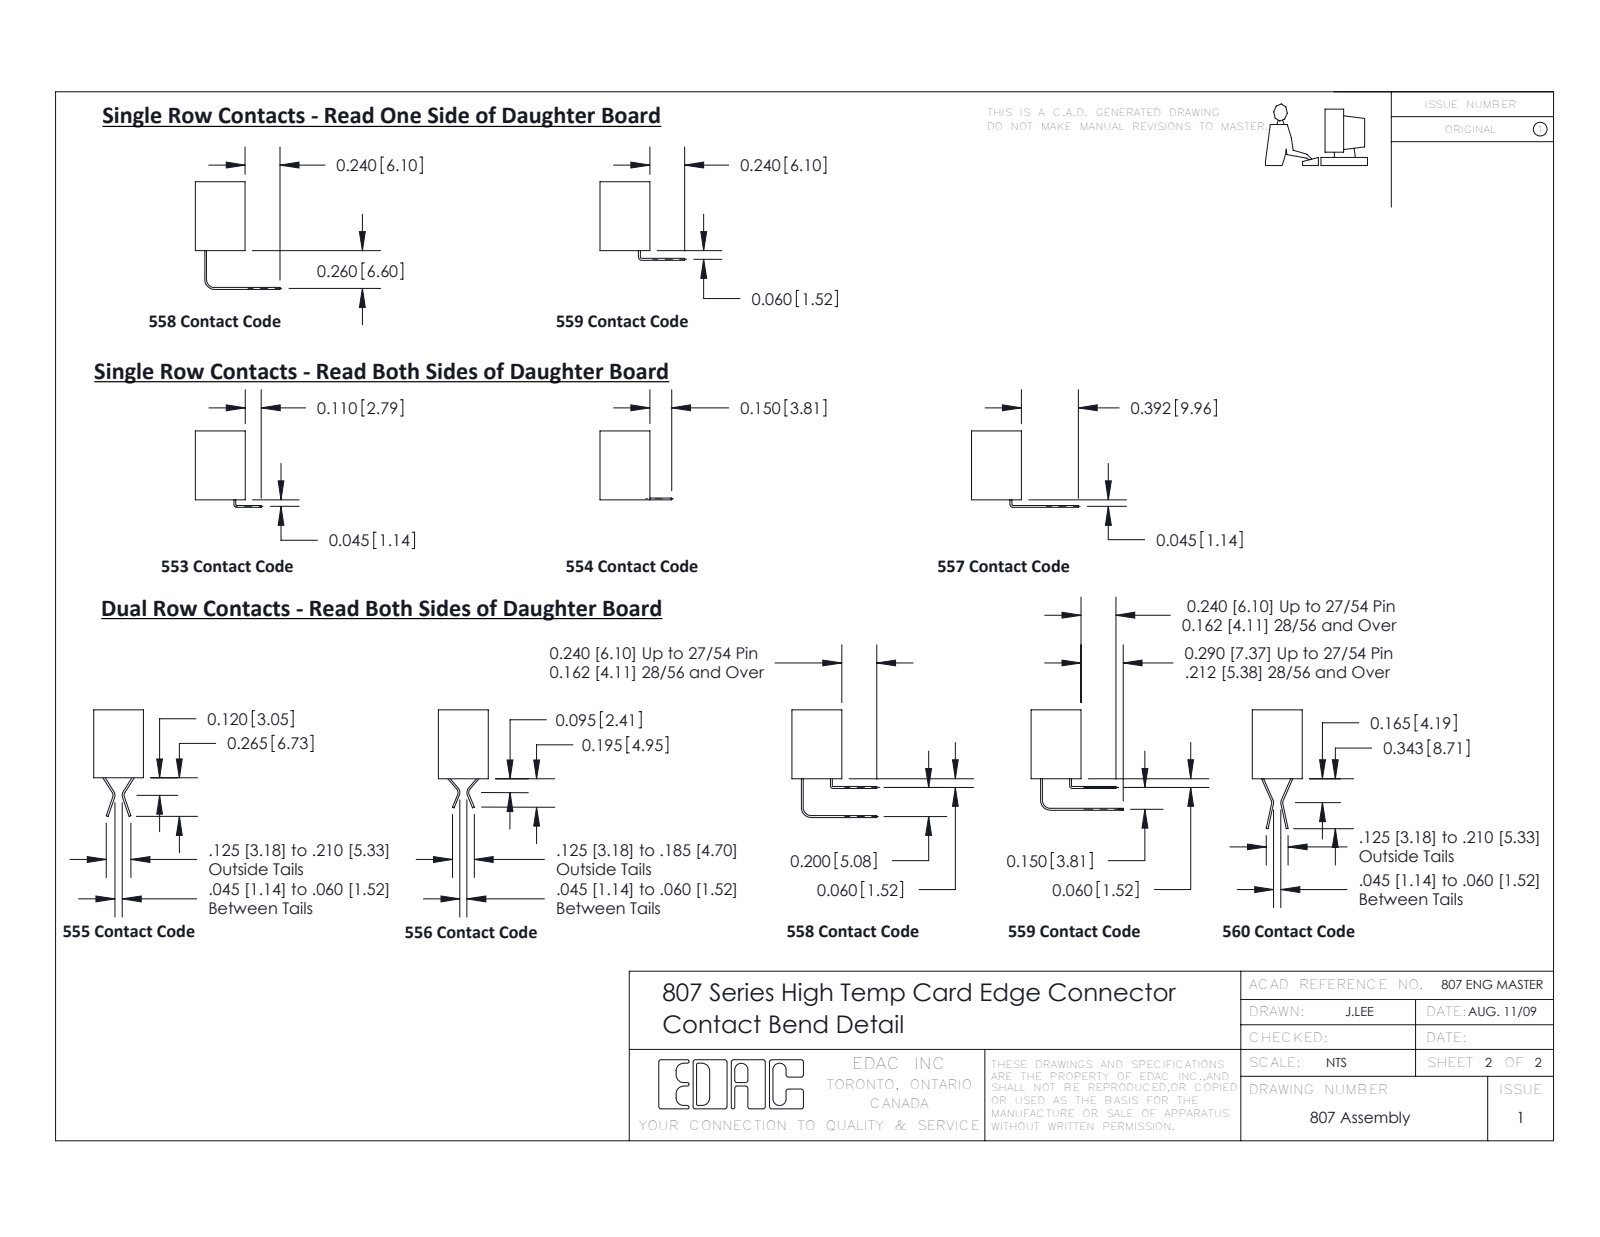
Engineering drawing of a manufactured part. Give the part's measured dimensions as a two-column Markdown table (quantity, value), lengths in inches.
| quantity | value |
| --- | --- |
| part name | 307-290-001_505; 357-006-405-101; 307 Part_No Mounting Lugs |
| STEP written by | SolidWorks 2020 (CONFIG_CONTROL_DESIGN) |
| units | inches |
| bodies | 7 solids, 453 faces (282 planar, 157 cylindrical, 14 other) |
| overall size | 1.246 × 0.755 × 0.343 |
| volume | 0.137 in³ |
| surface area | 5.021 in² |
| partial cylindrical surfaces (radius × count) | 0.02 × 23, 0.01 × 22, 0.03 × 12, 0.007 × 6, 0.031 × 6, 0.062 × 6, 0.026 × 3, 0.046 × 2 |
| main face-to-face distances | 0.343, 0.278, 0.065, 0.156, 0.013, 0.078, 0.265, 0.246, 0.141, 0.202 |
